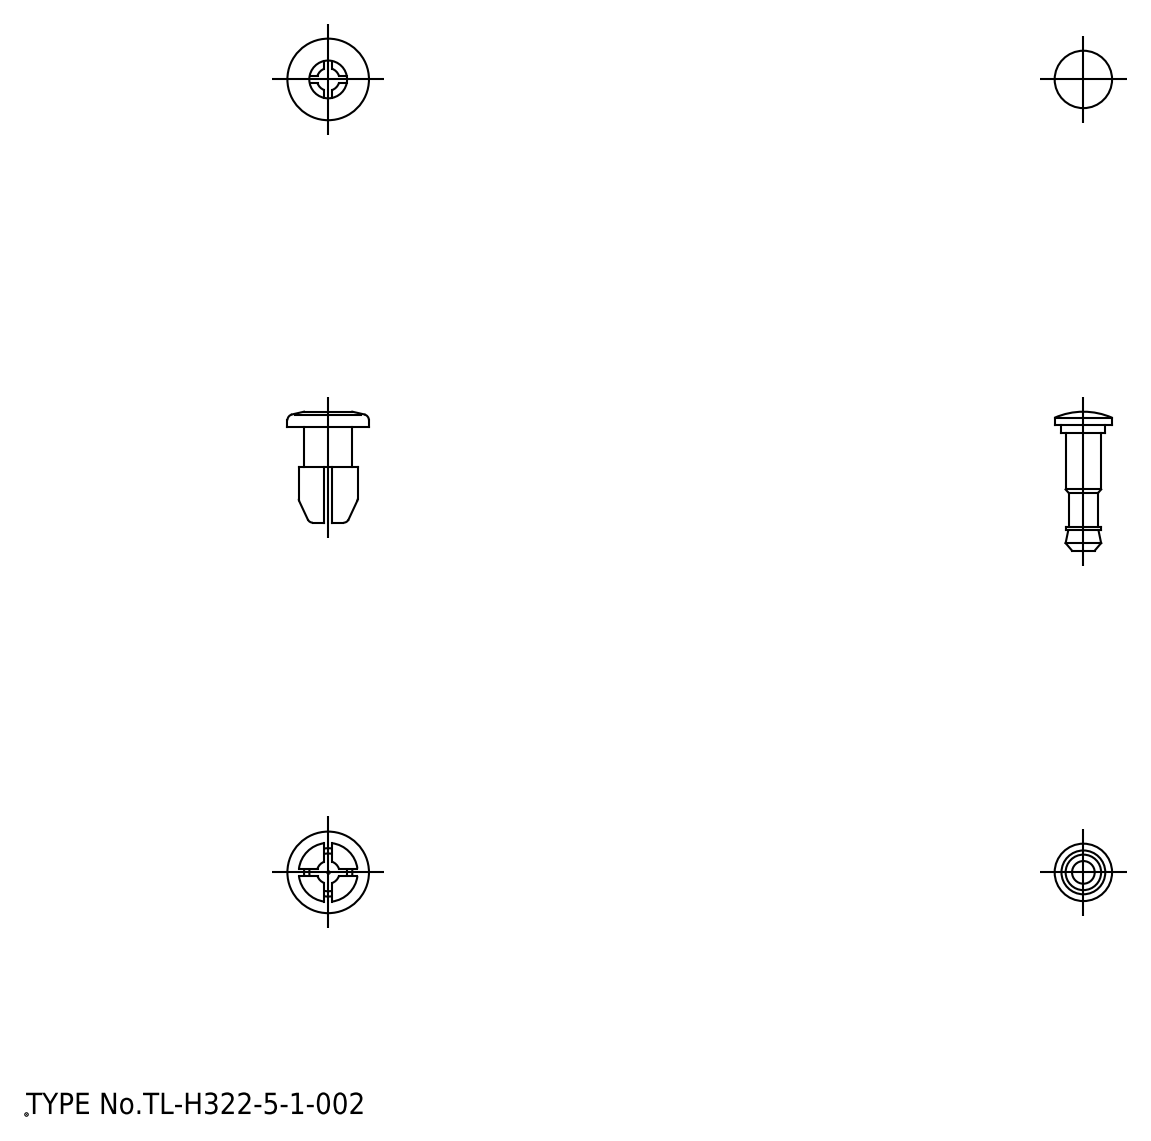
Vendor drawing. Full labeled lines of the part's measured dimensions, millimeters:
Part name (STEP PRODUCT): grommet; plunger
STEP written by: spGate 18.9.1 (****-****-****-****) (AUTOMOTIVE_DESIGN)
Units: millimetres
Bodies: 2 solids, 79 faces (27 planar, 24 cylindrical, 28 other)
Overall size (bounding box): 20.4 × 10.8 × 10.8
Volume: 667 mm³ · Surface area: 1 080 mm²
Round holes (diameter × count): ⌀5 ×1
Round bosses / shafts (diameter × count): ⌀10.8 ×1, ⌀7.8 ×1, ⌀7.6 ×1, ⌀6.4 ×1, ⌀5.8 ×1, ⌀4.7 ×1, ⌀3.8 ×1
Partial cylindrical surfaces — rounded edges, fillets, slot ends (radius × count): R1.5 ×1
Main face-to-face distances: 1, 5.9, 2, 5.3, 11.2, 7.3, 3.9, 12.7, 2.7, 10.2
